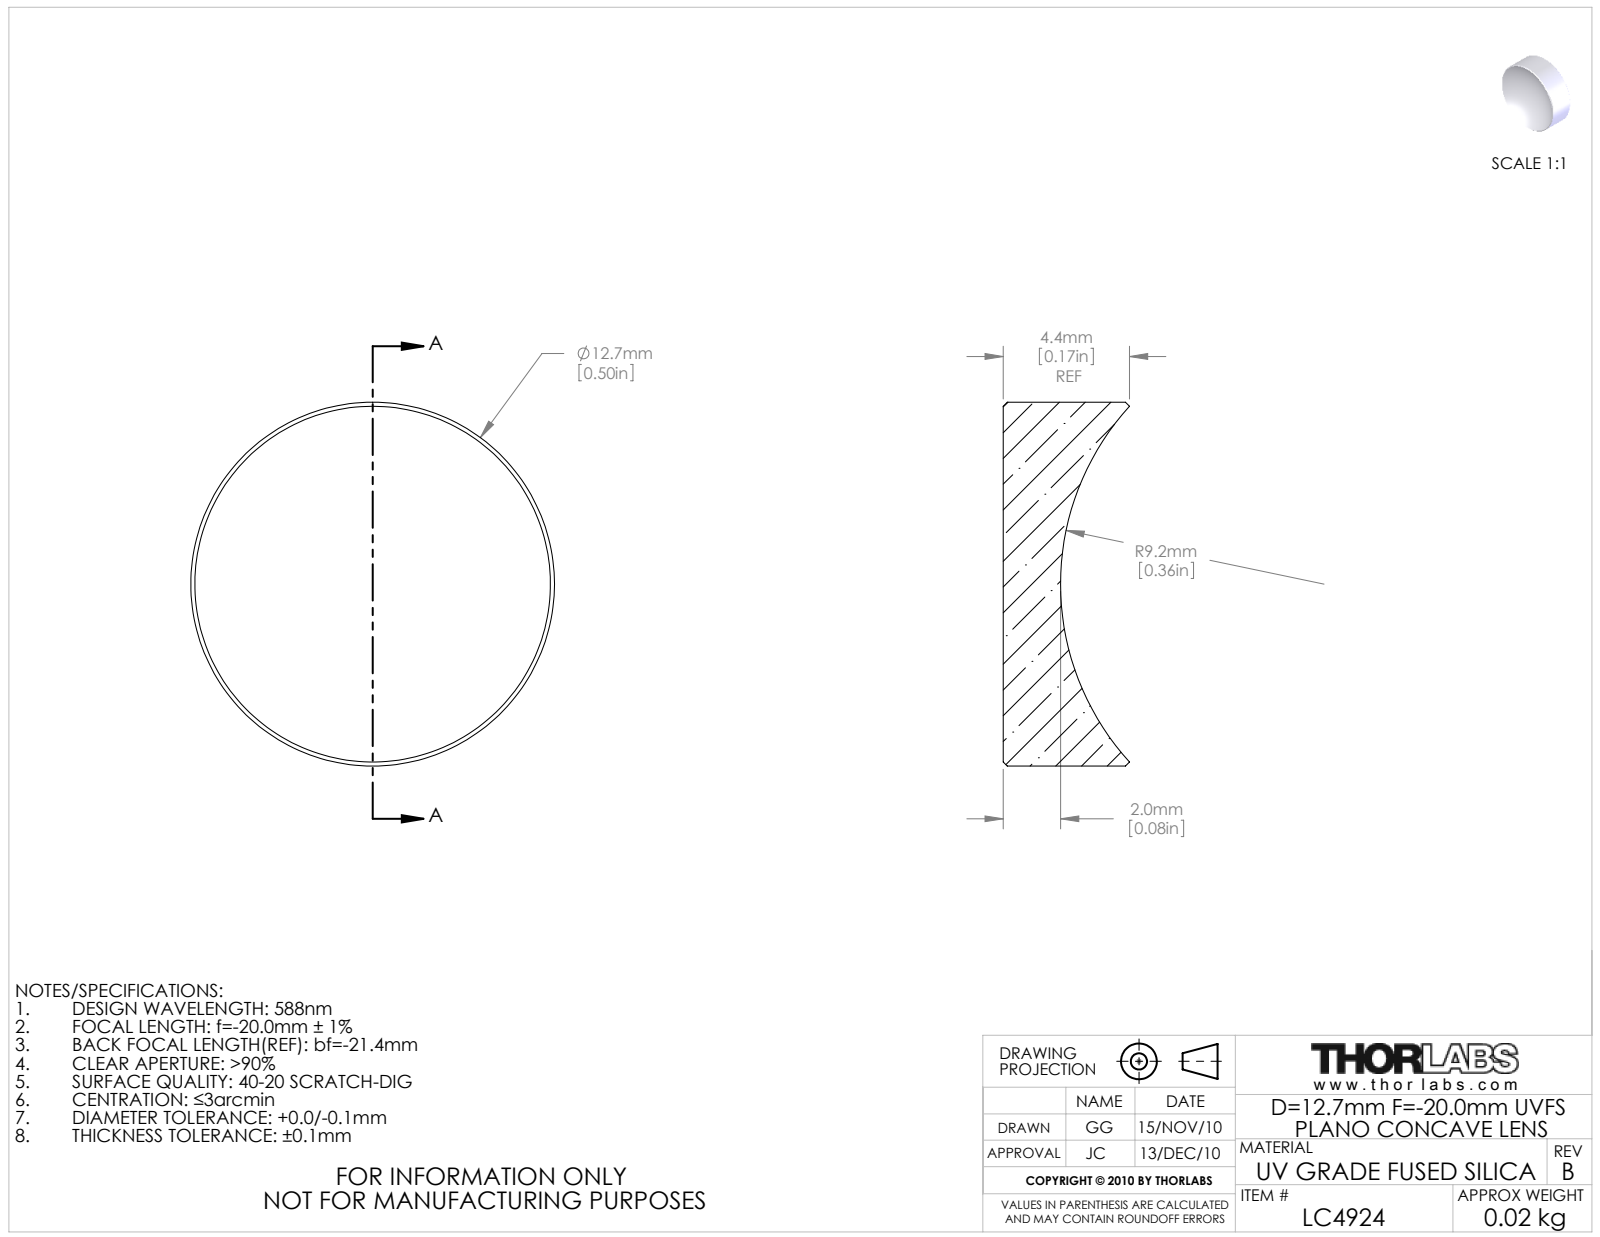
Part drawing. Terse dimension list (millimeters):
name: 3494-E0W
written by: SolidWorks 2009 (AUTOMOTIVE_DESIGN)
unit: mm
bodies: 1 solid, 9 faces (1 planar, 2 cylindrical, 6 other)
size: 12.7 × 12.7 × 4.41
volume: 405 mm³; area: 441 mm²
bosses: 1× ⌀12.7
